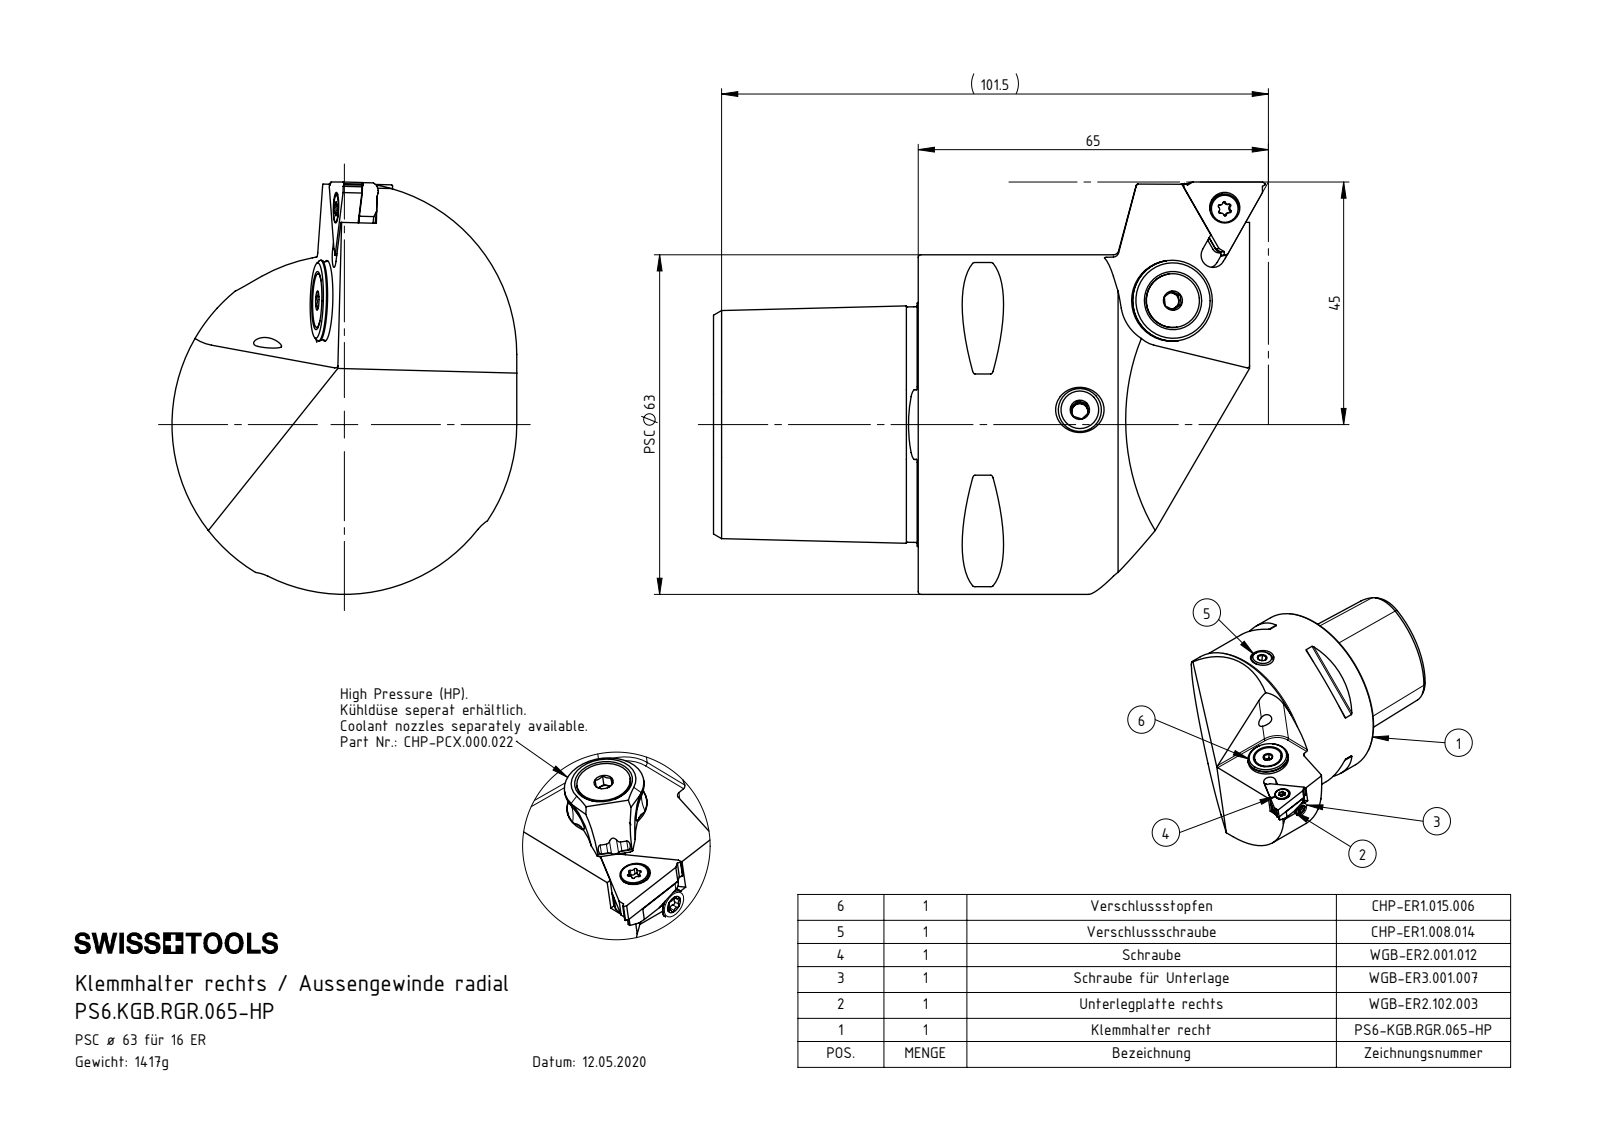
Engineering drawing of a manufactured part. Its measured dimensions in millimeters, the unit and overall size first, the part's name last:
Units: millimetres
Overall size (bounding box): 102.41 × 76.5 × 64
Round holes (diameter × count): ⌀2.58 ×2, ⌀4 ×2, ⌀4.2 ×2, ⌀5 ×2, ⌀1.2 ×1, ⌀2 ×1, ⌀2.5 ×1, ⌀3 ×1, ⌀4.02 ×1, ⌀5.2 ×1, ⌀7 ×1, ⌀8.1 ×1
Round bosses / shafts (diameter × count): ⌀5.5 ×3, ⌀63 ×1, ⌀15 ×1, ⌀13.4 ×1, ⌀10 ×1, ⌀8 ×1, ⌀5 ×1, ⌀3.18 ×1
Partial cylindrical surfaces — rounded edges, fillets, slot ends (radius × count): R0.5 ×10, R0.23 ×6, R0.34 ×6, R0.57 ×6, R0.57 ×6, R0.1 ×2, R32 ×2, R0.25 ×1
Main face-to-face distances: 38, 24.88, 27, 11, 1.46, 55.8, 6.53, 1.74, 4.79, 37.8
Hole centre spacings: 4.51, 4.5, 4.52, 16.08, 16.1, 16.24, 16.26, 19.83
Volume: 180 499 mm³ · Surface area: 32 299 mm²
Bodies: 10 solids, 310 faces (127 planar, 83 cylindrical, 100 other)
Part name (STEP PRODUCT): WGB-ER2.102.003_A; CHP-ER1.015.006; WGB-ER3.001.007_A; CHP-ER1.015.006_A (+8 more)
STEP written by: SolidWorks 2017 (AUTOMOTIVE_DESIGN)
